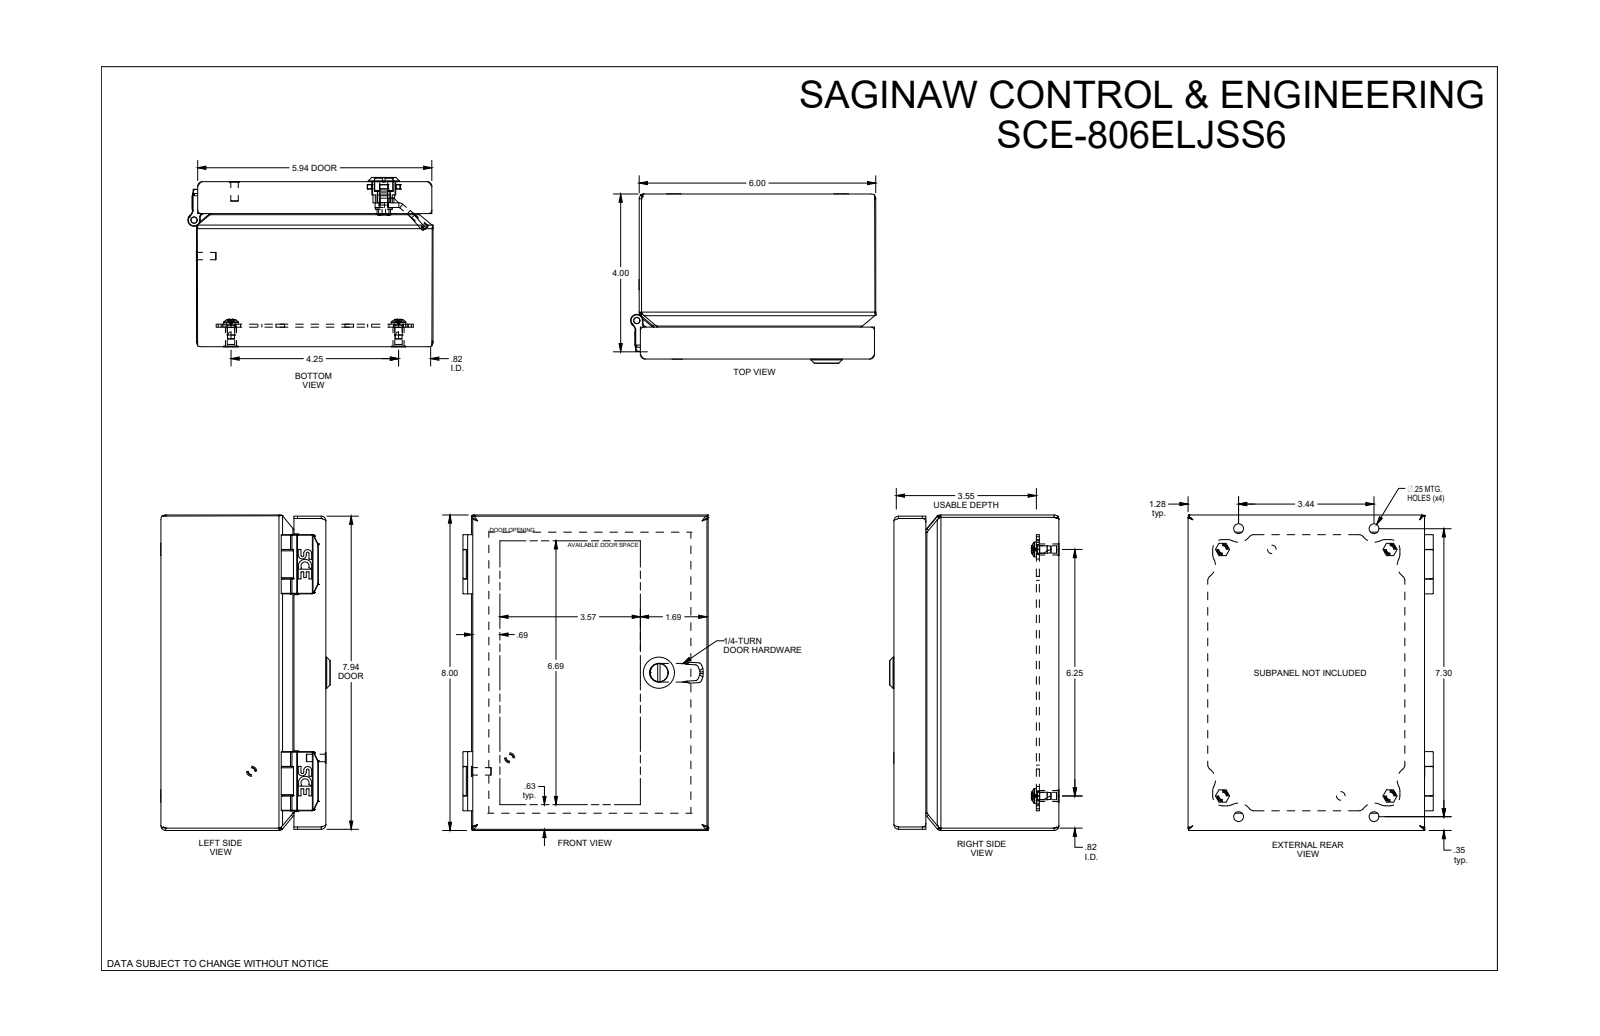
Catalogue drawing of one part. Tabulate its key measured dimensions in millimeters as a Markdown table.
| quantity | value |
| --- | --- |
| part name | SCE-806ELJSS6 |
| STEP written by | SolidWorks 2019 (CONFIG_CONTROL_DESIGN) |
| units | millimeters |
| bodies | 0 solids, 2717 faces (863 planar, 790 cylindrical, 1064 other) |
| overall size | 203.2 × 158 × 109.1 |
| round holes (diameter × count) | 6.4 × 8, 4.8 × 4, 7.2 × 4, 12.2 × 4, 0.5 × 2, 2.5 × 2, 4.4 × 2, 5 × 2, 5.5 × 2, 6.8 × 2, 4 × 1, 5.1 × 1 |
| round bosses / shafts (diameter × count) | 4.8 × 6, 9.5 × 4, 7.1 × 4, 4.3 × 4, 4.1 × 4, 3.4 × 4, 2.7 × 4, 6.6 × 2 |
| partial cylindrical surfaces (radius × count) | 2.7 × 132, 0.1 × 131, 0.2 × 32, 0.2 × 26, 0.6 × 24, 0.8 × 24, 3 × 23, 1.5 × 22 |
| main face-to-face distances | 1.5, 1.5, 150.9, 104.7, 103.3, 106.3, 104.8, 201.7, 14.5, 13 |
| hole center spacings | 16.8, 98.6, 172.4, 197.8, 25.2, 31.8, 67.2, 76.2 |
